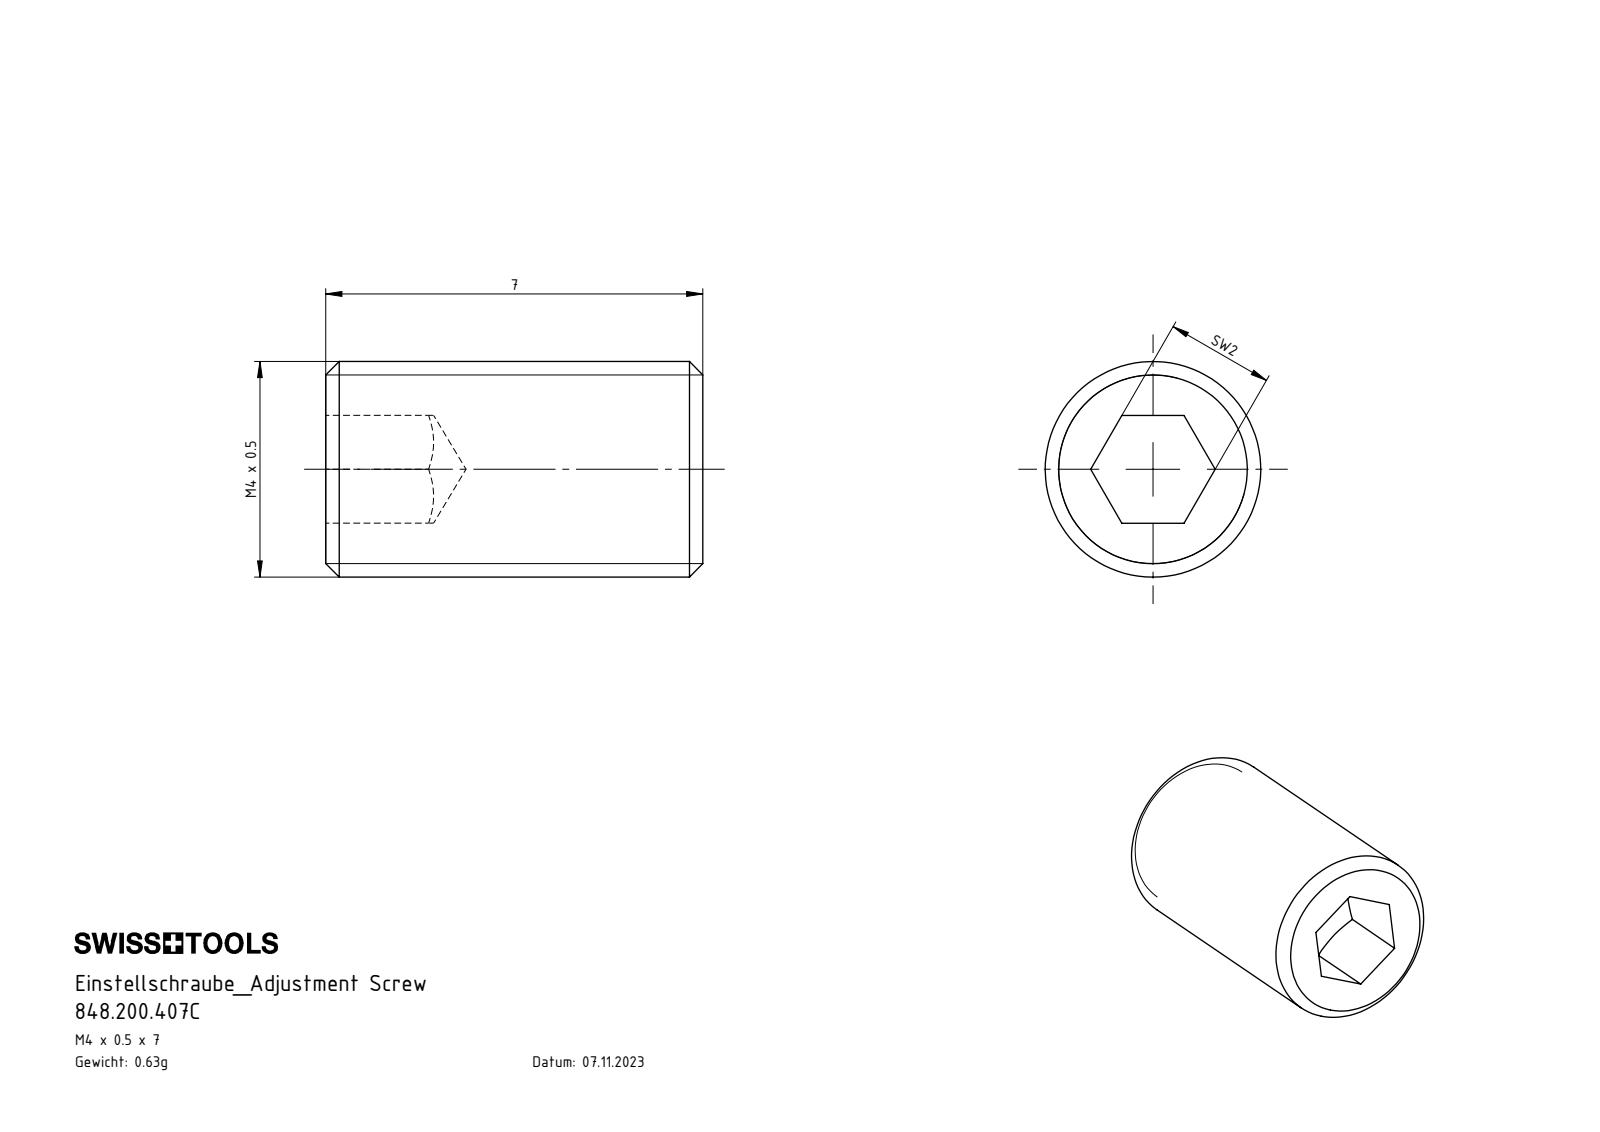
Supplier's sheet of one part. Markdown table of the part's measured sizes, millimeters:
| quantity | value |
| --- | --- |
| part name | 848.200.407C |
| STEP written by | SolidWorks 2022 (AUTOMOTIVE_DESIGN) |
| units | millimeters |
| bodies | 1 solid, 16 faces (8 planar, 2 cylindrical, 6 other) |
| overall size | 7 × 4 × 4 |
| volume | 80 mm³ |
| surface area | 123 mm² |
| round bosses / shafts (diameter × count) | 4 × 1 |
| main face-to-face distances | 2, 7 |
